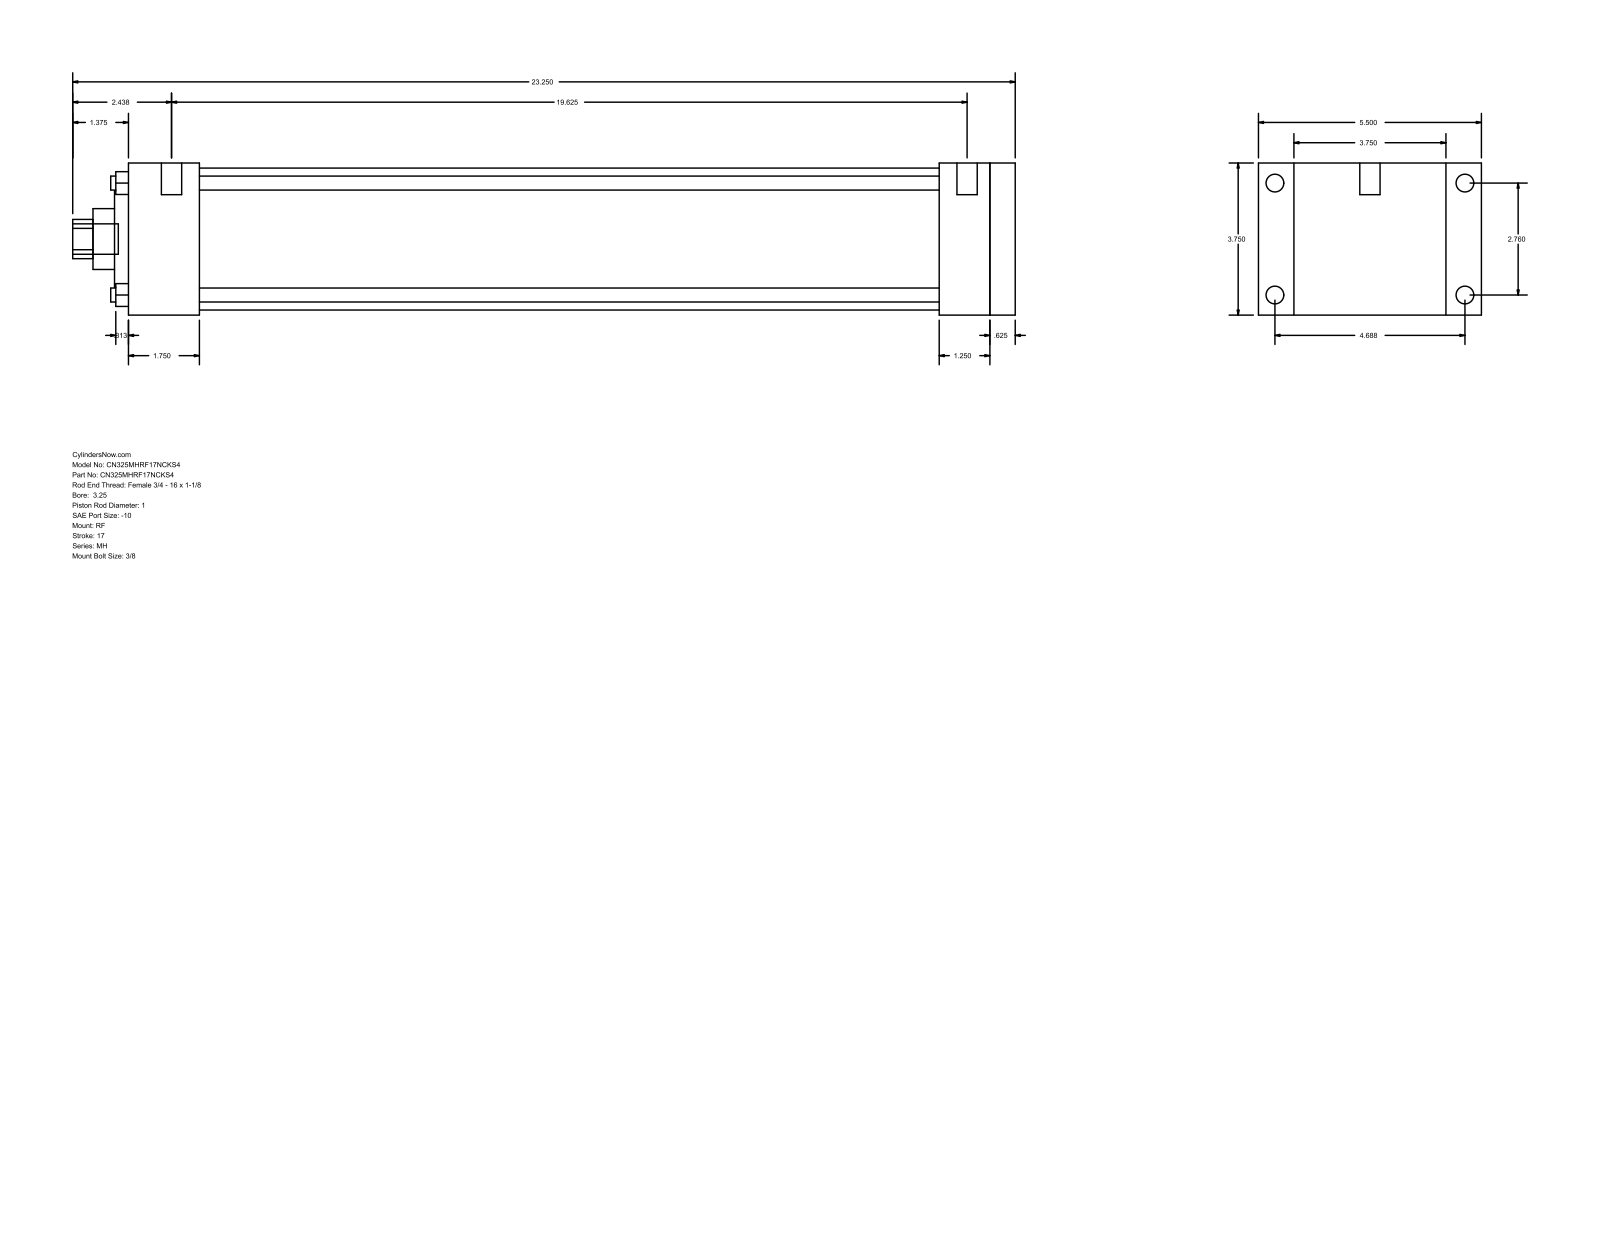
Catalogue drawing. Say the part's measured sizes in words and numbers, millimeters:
The part is named "MH_RF__0325_1". Its 3-D file was written by "GSSL Pune (CONFIG_CONTROL_DESIGN)". It is 0 solids with 94 faces: 65 planar, 29 cylindrical and 0 other. Overall it measures 590.55 by 139.7 by 95.25 millimeters. Round holes: 4 of diameter 8.76, 1 of diameter 25.4, 1 of diameter 38.1, 1 of diameter 60.33, 1 of diameter 88.9. Round bosses or shafts: 4 of diameter 11.13, 4 of diameter 5.56, 2 of diameter 12.7, 1 of diameter 19.05. Partial cylindrical surfaces (rounded edges, fillets, slot ends): 1 of radius 12.29. The main face-to-face distances are 95.24, 555.63, 539.75, 15.88, 22.23, 117.47, 44.46, 495.29, 511.17, 508. The hole center spacings are 49.57, 70.1, 99.14.
